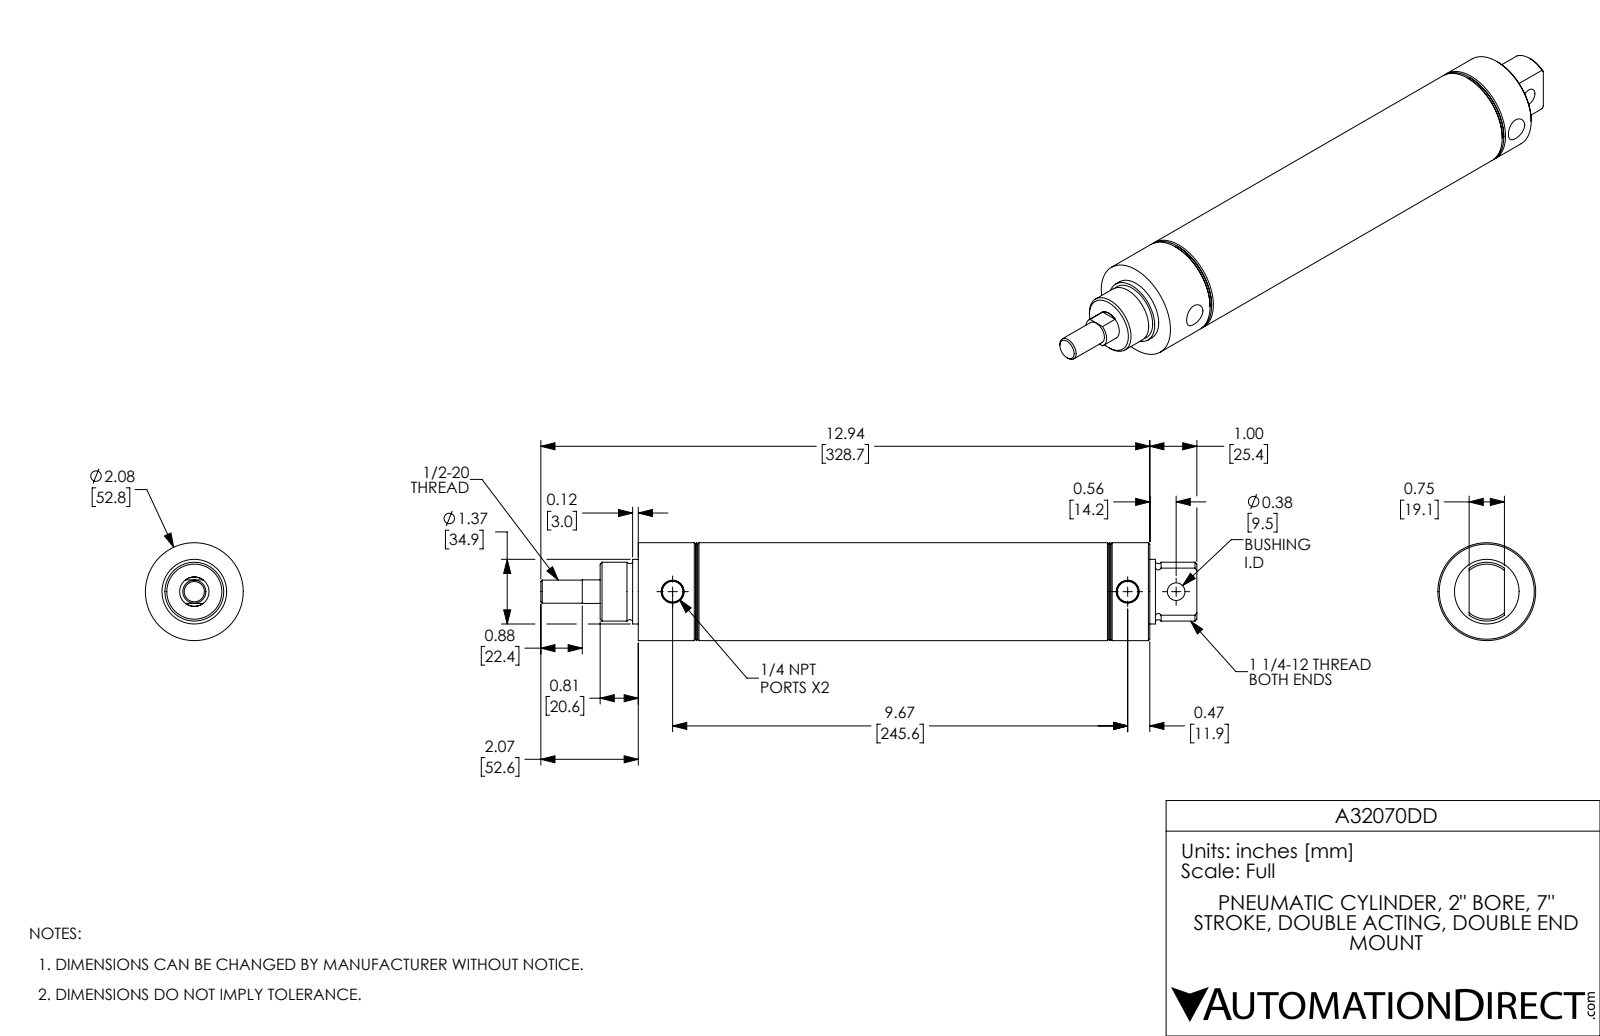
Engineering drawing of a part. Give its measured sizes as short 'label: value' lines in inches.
name: A32070DD; A32070DD-Rod; A32070DD-MainBody
written by: SolidWorks 2017 (AUTOMOTIVE_DESIGN)
unit: in
bodies: 2 solids, 88 faces (20 planar, 30 cylindrical, 38 other)
size: 13.94 × 2.08 × 2.08
volume: 18.92 in³; area: 175.7 in²
holes: 2× ⌀0.438, 1× ⌀0.375, 1× ⌀0.625, 1× ⌀2
bosses: 1× ⌀2.08, 1× ⌀1.373, 1× ⌀1.25, 1× ⌀0.491
face distances: 1.685, 9.185, 0.5, 7.5, 7, 8.685, 2.185, 10.87, 0.12, 1.805
hole spacings: 1.03, 9.67, 10.7
